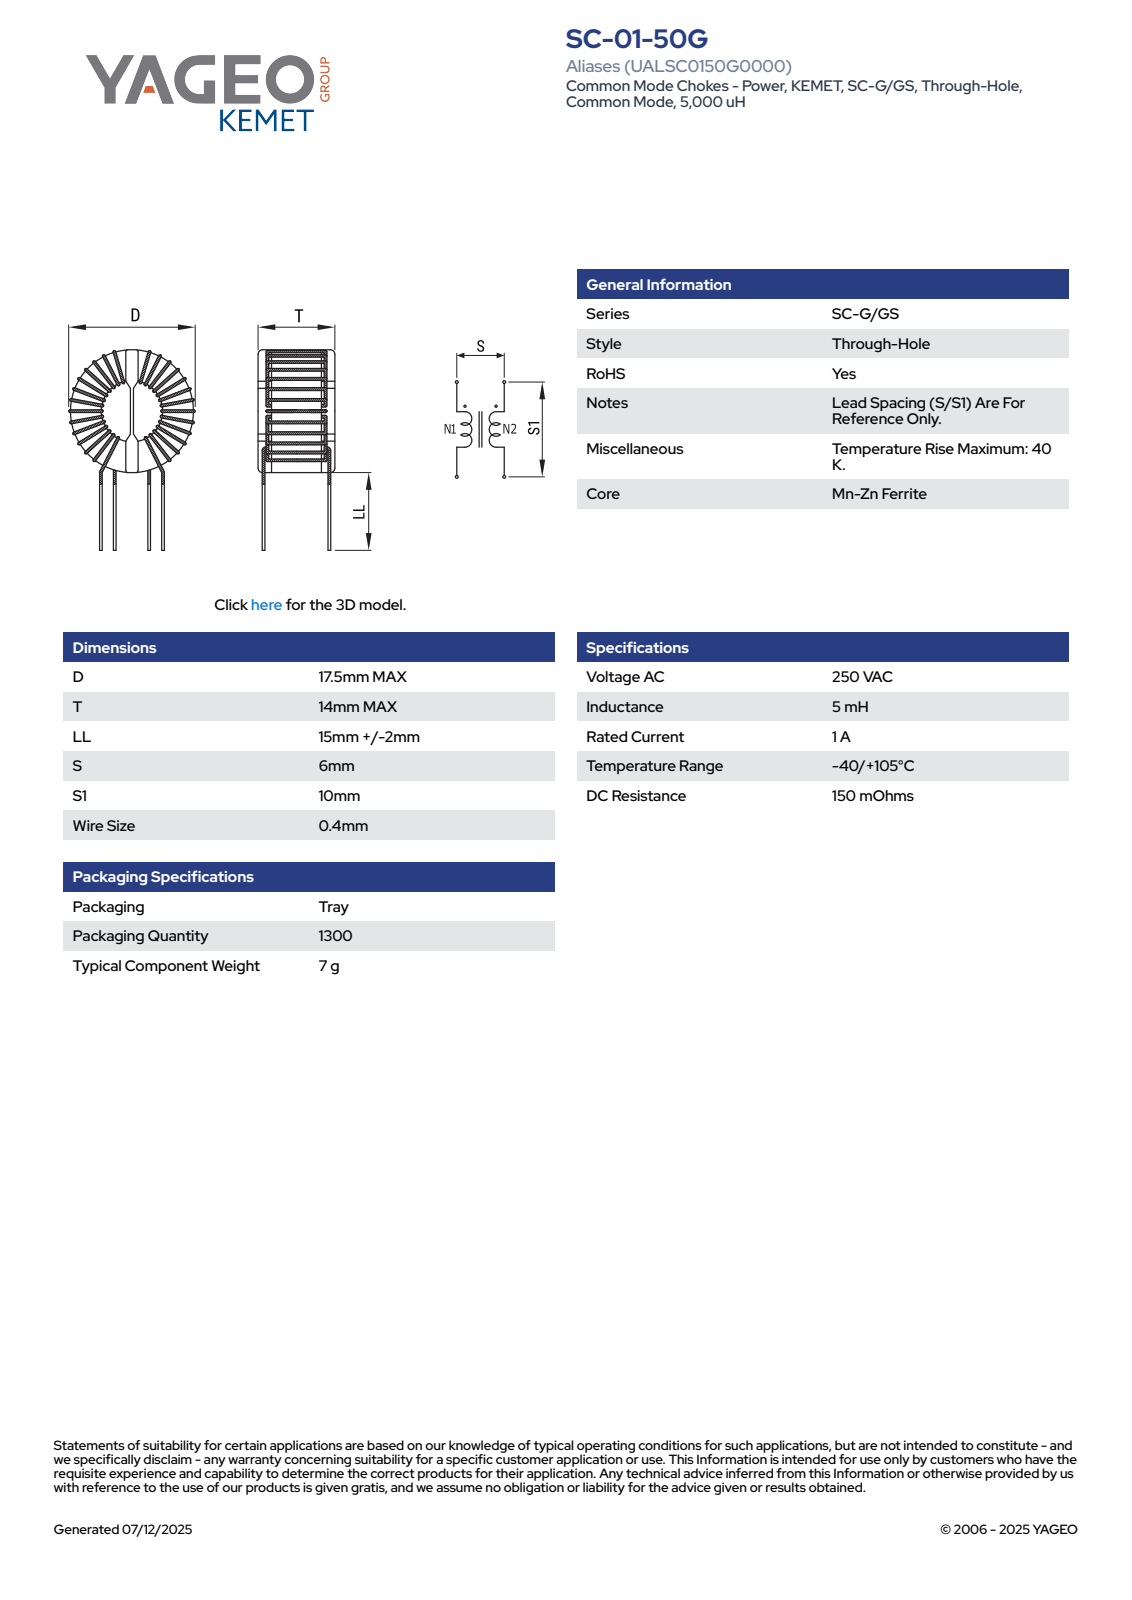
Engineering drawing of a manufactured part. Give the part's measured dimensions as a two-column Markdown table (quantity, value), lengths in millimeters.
| quantity | value |
| --- | --- |
| part name | SC-01-50G |
| STEP written by | SolidWorks 2018 (AUTOMOTIVE_DESIGN) |
| units | millimeters |
| bodies | 1 solid, 268 faces (121 planar, 65 cylindrical, 82 other) |
| overall size | 30.37 × 17.5 × 14 |
| volume | 1 786 mm³ |
| surface area | 1 710 mm² |
| round bosses / shafts (diameter × count) | 0.4 × 8 |
| partial cylindrical surfaces (radius × count) | 0.2 × 16, 2.32 × 1, 3.21 × 1, 3.62 × 1, 3.67 × 1, 3.8 × 1, 6.35 × 1, 6.4 × 1 |
| main face-to-face distances | 1.2, 2, 8.3, 0.8, 3.2, 2.85, 11.15, 1.15, 2.05, 0.85 |
